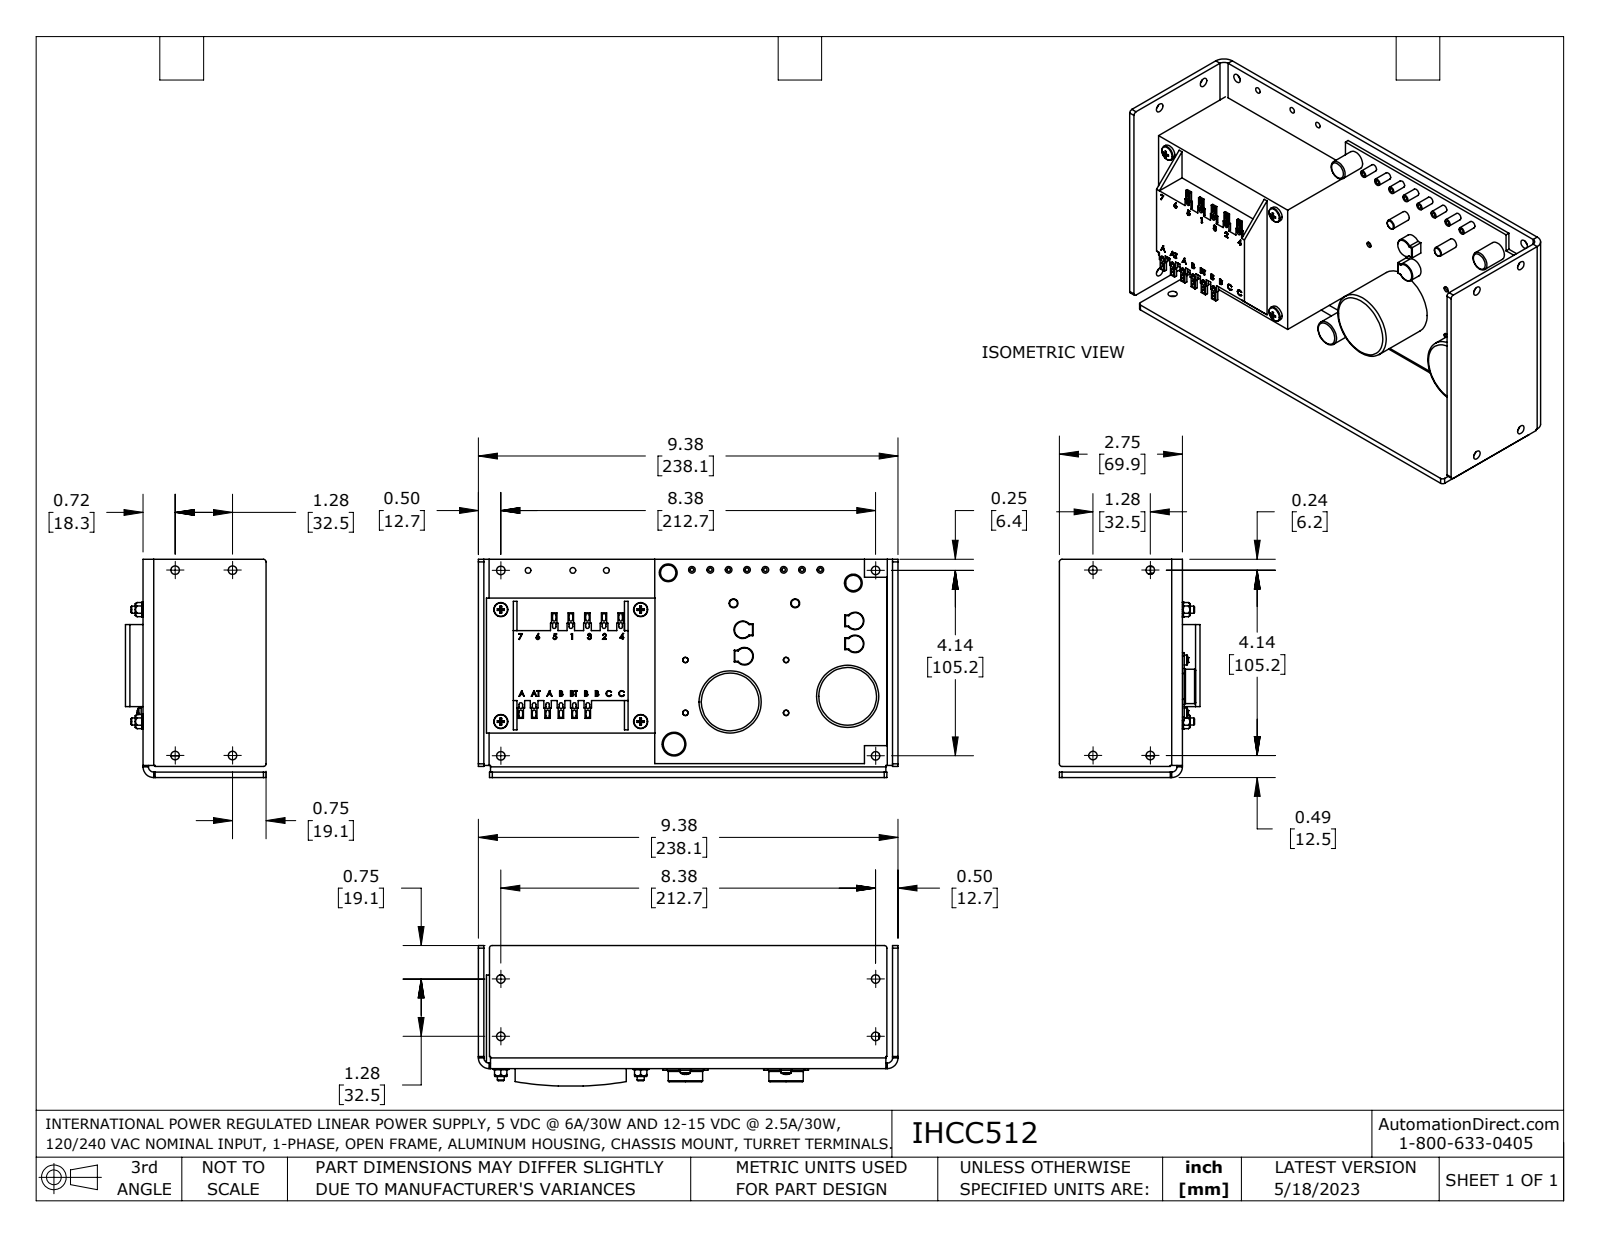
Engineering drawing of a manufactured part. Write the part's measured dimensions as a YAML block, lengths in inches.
part_name: "IHCC512"
step_written_by: "SolidWorks 2021 (AUTOMOTIVE_DESIGN)"
units: inches
bodies: {solids: 21, faces: 1122, planar: 682, cylindrical: 278, other: 162}
overall_size: [9.375, 4.875, 3.14]
volume: 44.3
surface_area: 325.7
round_holes:
  - {diameter: 0.189, count: 12}
  - {diameter: 0.079, count: 8}
  - {diameter: 0.115, count: 4}
  - {diameter: 0.12, count: 4}
  - {diameter: 0.13, count: 4}
  - {diameter: 0.157, count: 4}
  - {diameter: 0.169, count: 4}
  - {diameter: 0.128, count: 3}
round_bosses_or_shafts:
  - {diameter: 0.15, count: 8}
  - {diameter: 0.315, count: 4}
  - {diameter: 0.25, count: 4}
  - {diameter: 0.22, count: 4}
  - {diameter: 0.118, count: 4}
  - {diameter: 1.39, count: 2}
  - {diameter: 0.768, count: 2}
  - {diameter: 0.398, count: 2}
partial_cylinders:
  - {radius: 0.04, count: 44}
  - {radius: 0.012, count: 10}
  - {radius: 0.06, count: 8}
  - {radius: 0.126, count: 4}
  - {radius: 0.162, count: 4}
  - {radius: 0.167, count: 4}
  - {radius: 0.197, count: 4}
  - {radius: 0.118, count: 3}
face_to_face_distances: [0.122, 0.197, 0.319, 9.253, 0.276, 0.079, 0.398, 9.375, 9.131, 1.772]
hole_center_spacings: [0.82, 0.41, 1.23, 1.281, 8.375, 0.41, 2.05, 1.181]
